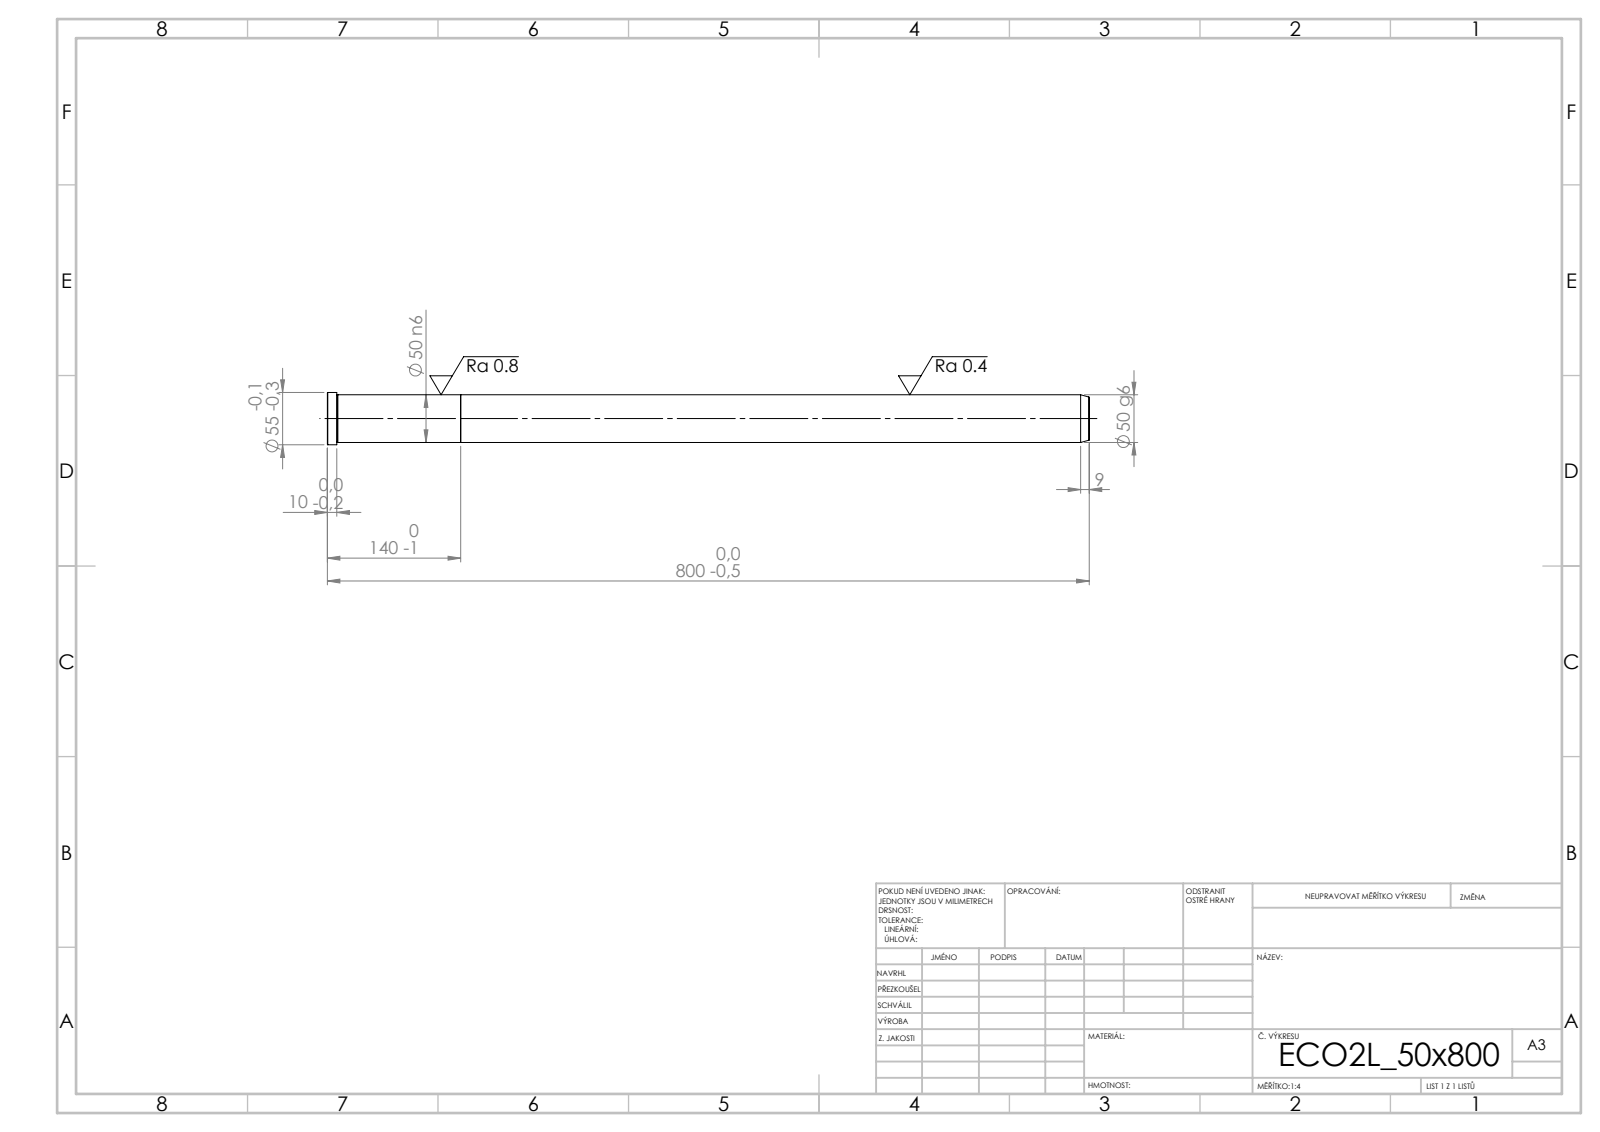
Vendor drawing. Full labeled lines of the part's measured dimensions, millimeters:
STEP written by: SolidWorks 2019 (CONFIG_CONTROL_DESIGN)
Units: millimetres
Bodies: 2 solids, 21 faces (5 planar, 6 cylindrical, 10 other)
Overall size (bounding box): 800 × 55 × 55
Volume: 1 573 000 mm³ · Surface area: 134 138 mm²
Round bosses / shafts (diameter × count): ⌀55 ×1, ⌀50 ×1
Main face-to-face distances: 140, 660, 800, 790, 130, 10
